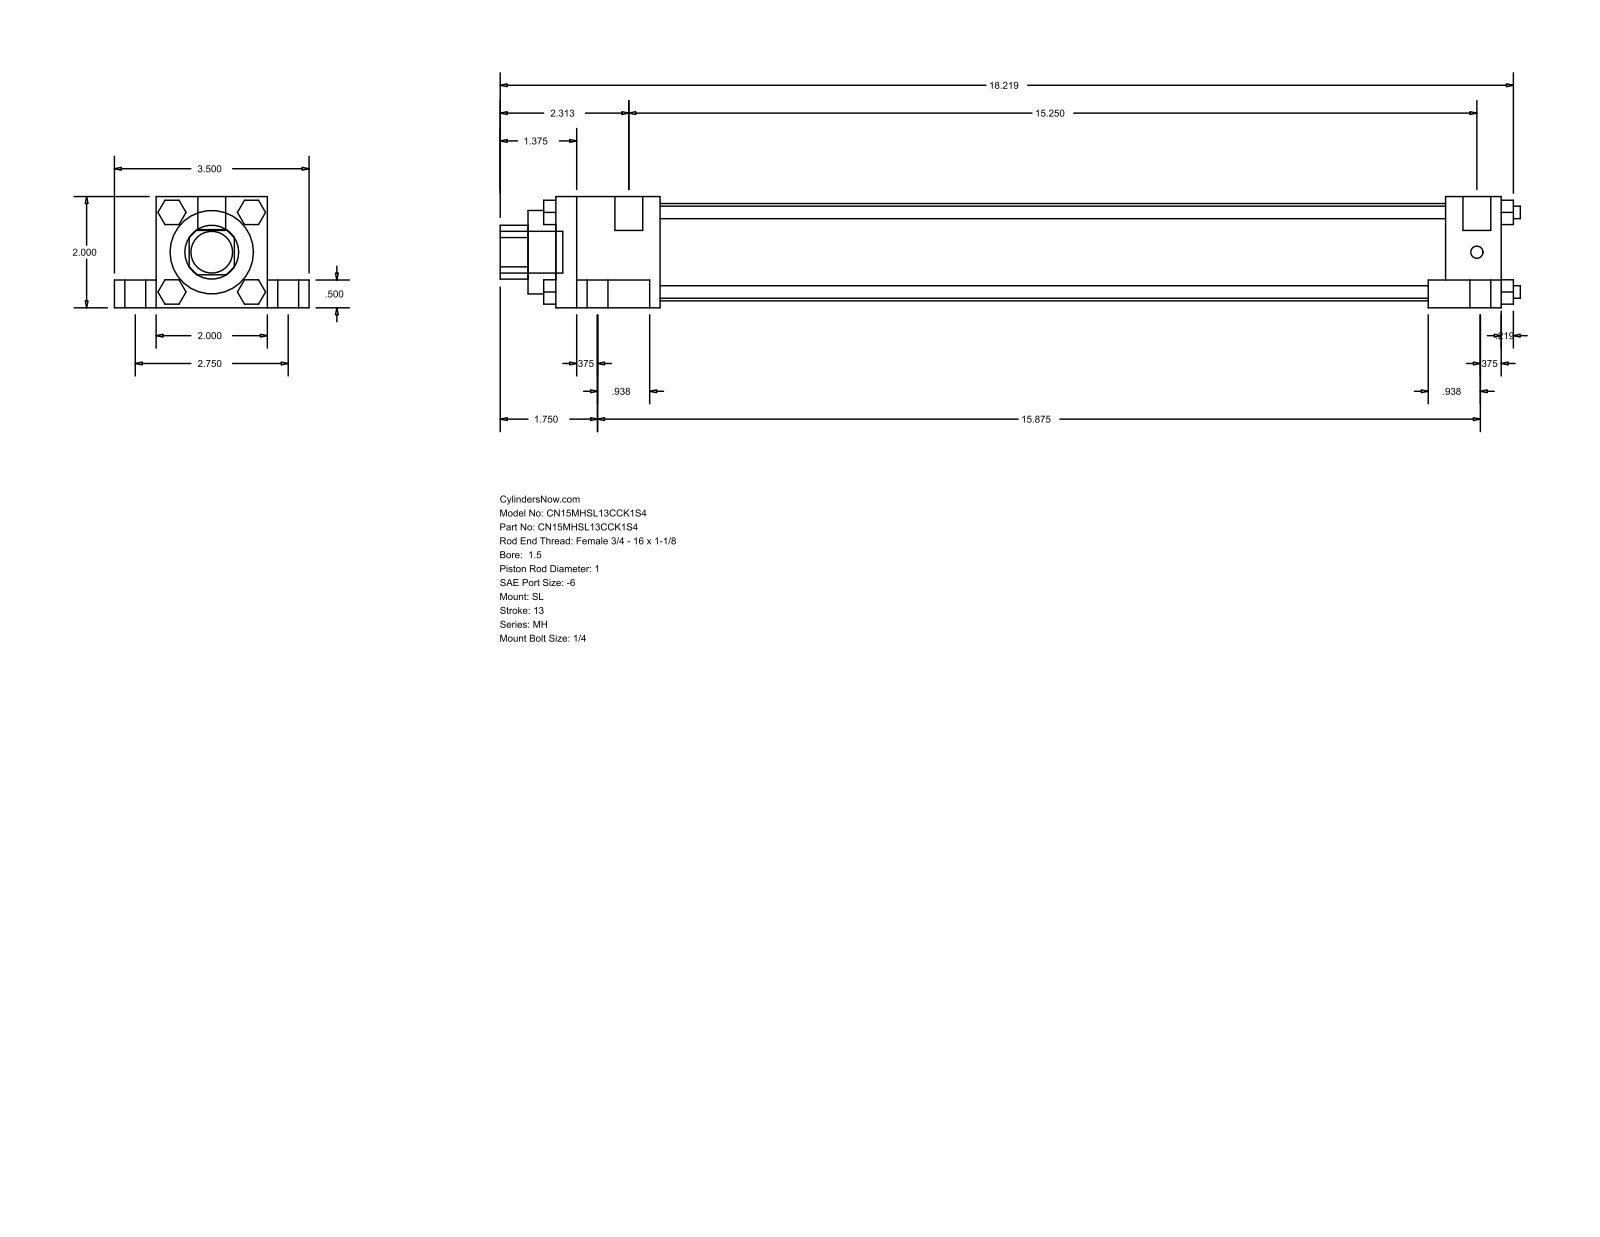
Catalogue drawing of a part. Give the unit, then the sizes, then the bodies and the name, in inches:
Units: inches
Overall size (bounding box): 18.344 × 3.5 × 2
Round holes (diameter × count): ⌀1 ×1, ⌀1.5 ×1, ⌀1.75 ×1
Round bosses / shafts (diameter × count): ⌀0.625 ×4, ⌀0.375 ×4, ⌀0.225 ×4, ⌀0.219 ×4, ⌀0.5 ×2, ⌀0.75 ×1
Partial cylindrical surfaces — rounded edges, fillets, slot ends (radius × count): R0.484 ×1
Main face-to-face distances: 2, 0.5, 1.5, 0.75, 2.75, 17, 1, 0.375, 1.313, 15.313
Bodies: 0 solids, 148 faces (112 planar, 36 cylindrical, 0 other)
Part name (STEP PRODUCT): MH_SL__0150_1
STEP written by: GSSL Pune (CONFIG_CONTROL_DESIGN)
